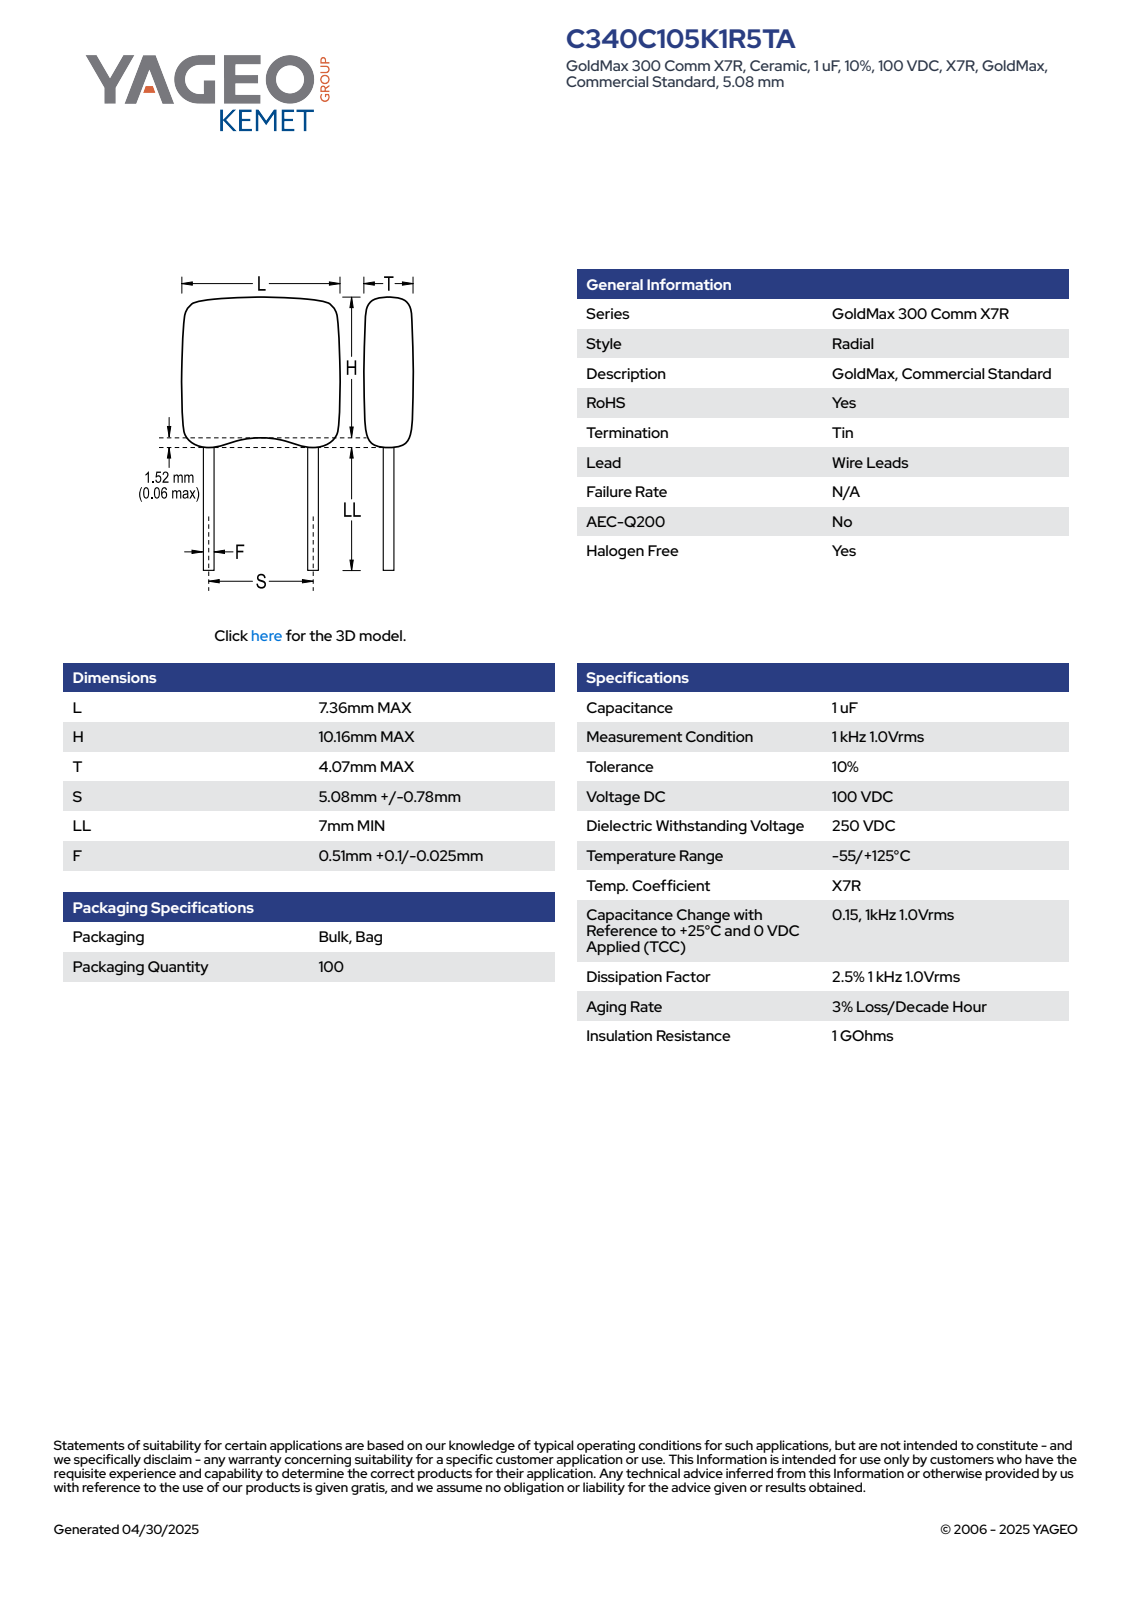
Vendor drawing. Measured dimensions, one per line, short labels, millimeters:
name: CCR_KRCST_C340_L7.36H10.16T4.07S5.08LL7F0.61
written by: SolidWorks 2014 (AUTOMOTIVE_DESIGN)
unit: mm
bodies: 4 solids, 83 faces (65 planar, 14 cylindrical, 4 other)
size: 18.68 × 7.36 × 4.08
volume: 344 mm³; area: 330 mm²
bosses: 2× ⌀0.61
rounds: 10× R0.75
face distances: 4.07, 7.36, 11.68, 4.08, 7, 18.68, 0.79, 13.25, 6.25, 5.43
